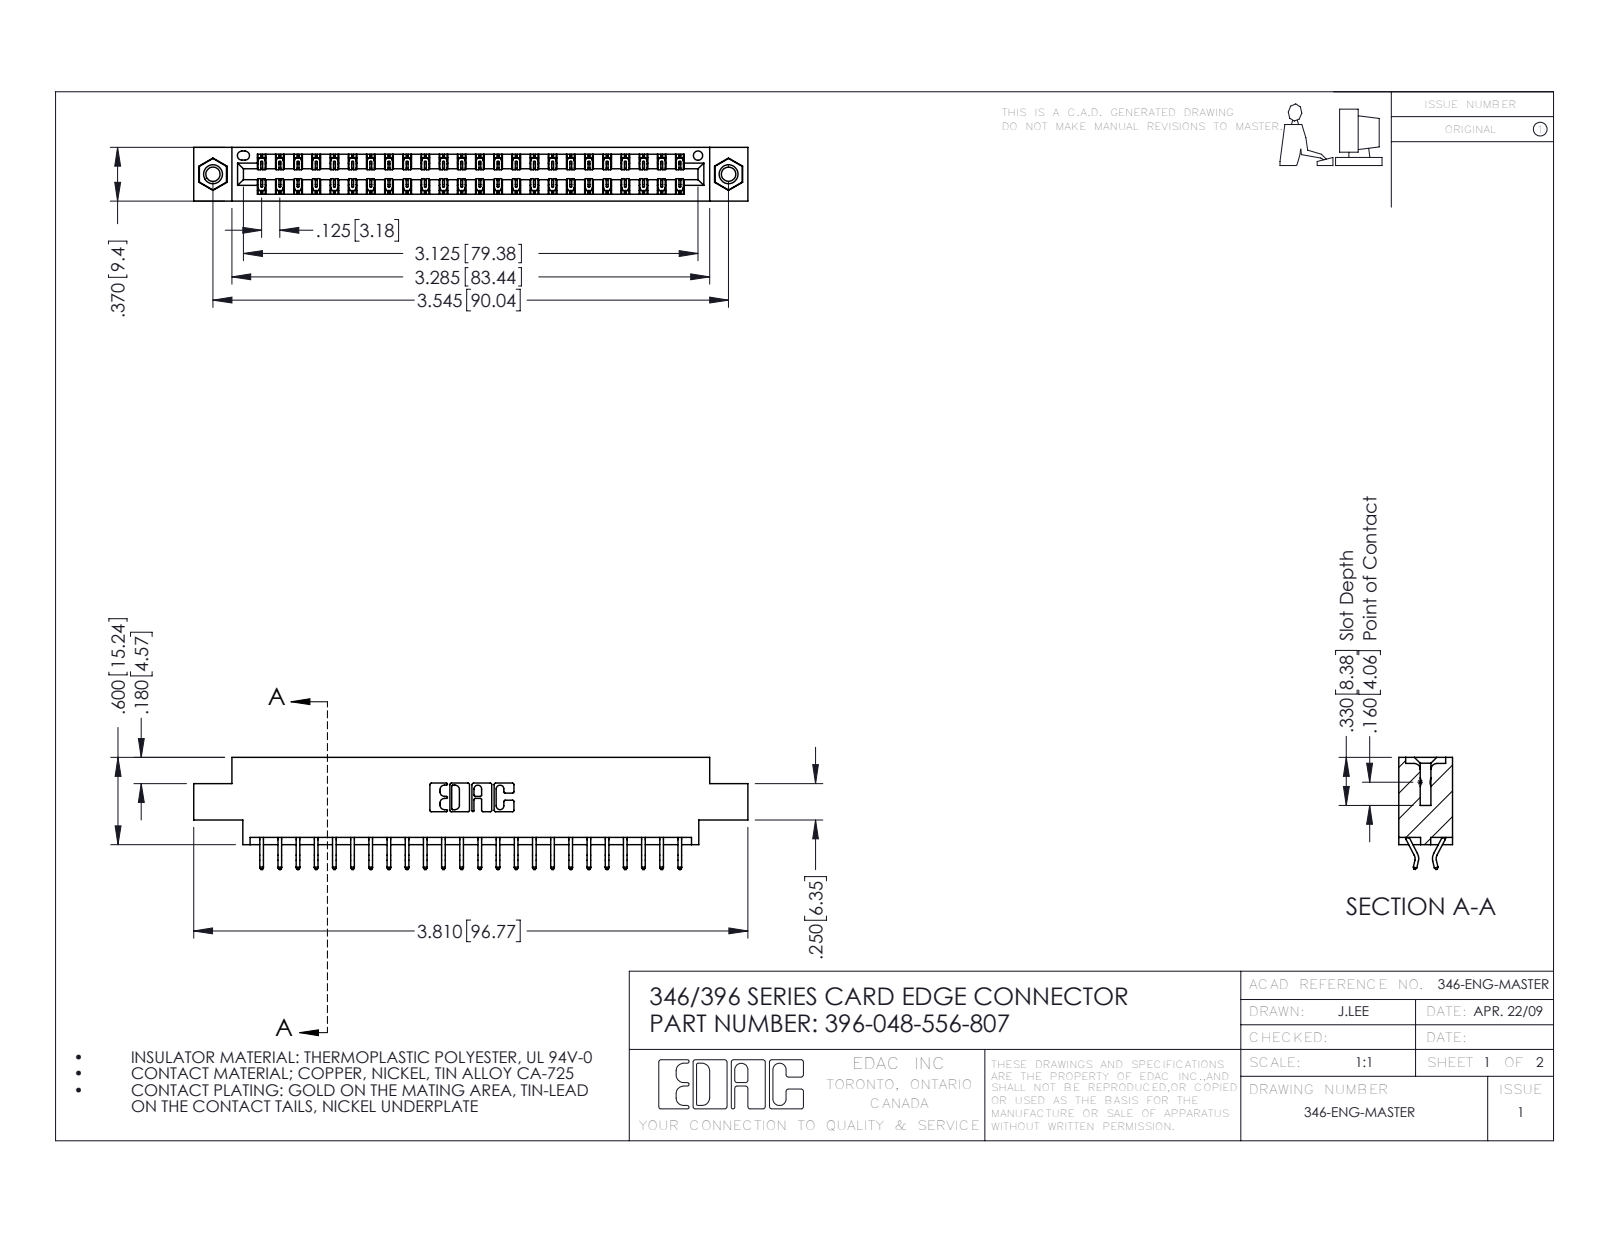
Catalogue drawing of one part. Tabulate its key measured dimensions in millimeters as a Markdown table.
| quantity | value |
| --- | --- |
| part name | 345-292-001_556 Tail; 345-250-001_345-250-005-103; 396-048-556-807; 346 Part_0.170 Offset - 0.156 Dia-TI |
| STEP written by | SolidWorks 2016 (CONFIG_CONTROL_DESIGN) |
| units | millimeters |
| bodies | 51 solids, 2970 faces (1984 planar, 970 cylindrical, 16 other) |
| overall size | 96.8 × 19.6 × 9.4 |
| volume | 9 130 mm³ |
| surface area | 12 430 mm² |
| round holes (diameter × count) | 2.5 × 2, 3.2 × 2, 4 × 2, 1.6 × 1 |
| round bosses / shafts (diameter × count) | 3.9 × 2 |
| partial cylindrical surfaces (radius × count) | 0.2 × 72, 0.3 × 22, 0.2 × 6, 0.8 × 6, 0.7 × 3, 0.3 × 2, 0.4 × 2, 0.6 × 2 |
| main face-to-face distances | 1.2, 8.2, 9.4, 6.4, 0.6, 1.8, 7.6, 7, 5.6, 3.8 |
| hole center spacings | 6.2, 84.8, 90 |
